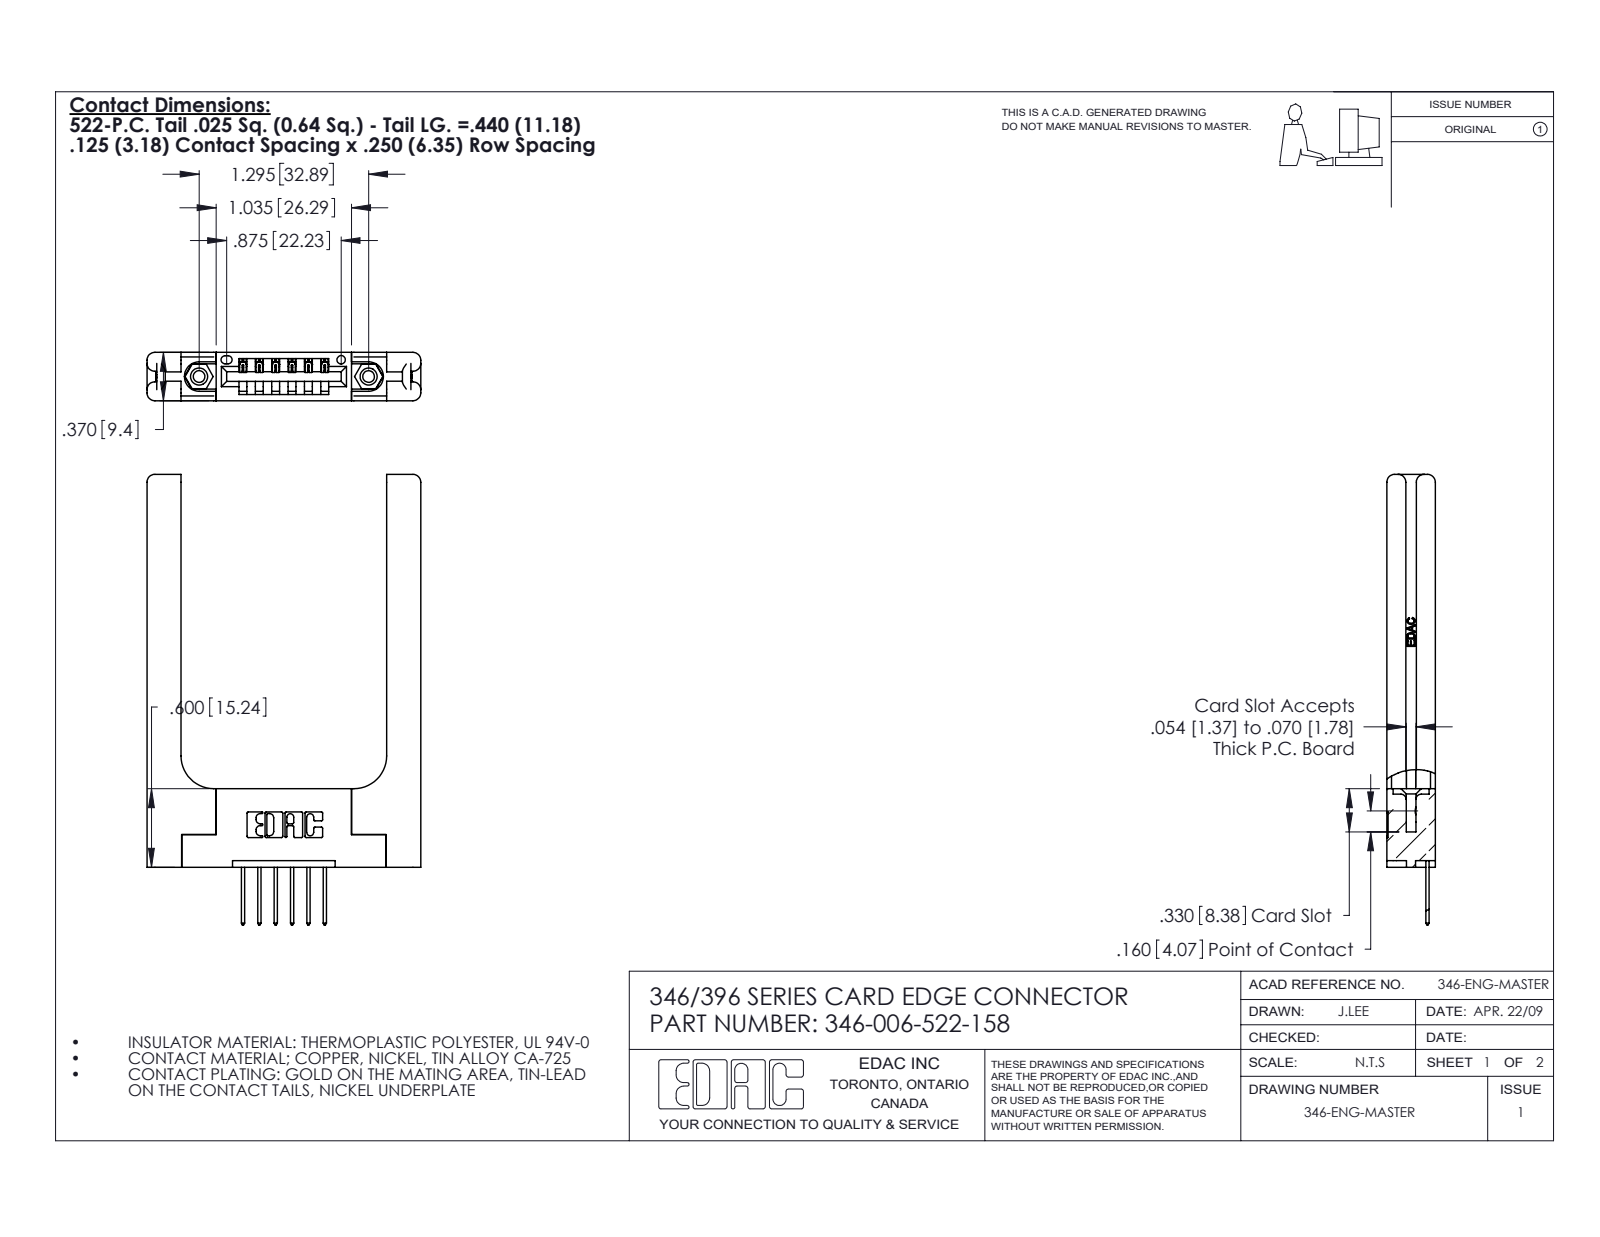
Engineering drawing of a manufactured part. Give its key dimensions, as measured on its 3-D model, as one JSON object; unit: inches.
{"part_name": "345-292-001_345-293-122; 346 Part_Flush Mounting Lugs - 0.156 Dia-TH; 346-006-522-158; 346-220-058_345-220-058 (+1 more)", "step_written_by": "SolidWorks 2020 (CONFIG_CONTROL_DESIGN)", "units": "inches", "bodies": {"solids": 11, "faces": 740, "planar": 478, "cylindrical": 202, "other": 60}, "overall_size": [3.44, 2.091, 0.37], "volume_in3": 0.753, "surface_area_in2": 16.83, "round_holes": [[0.089, 2], [0.125, 2], [0.156, 2], [0.064, 1]], "round_bosses_or_shafts": [[0.155, 2]], "partial_cylinders_radius": [[0.01, 22], [0.06, 16], [0.006, 12], [0.01, 12], [0.007, 6], [0.031, 6], [0.026, 3], [0.03, 2]], "face_to_face_distances": [0.37, 0.15, 0.22, 0.072, 0.25, 0.148, 1.571, 0.048, 0.322, 0.102], "hole_center_spacings": [0.246, 1.092, 1.295]}
